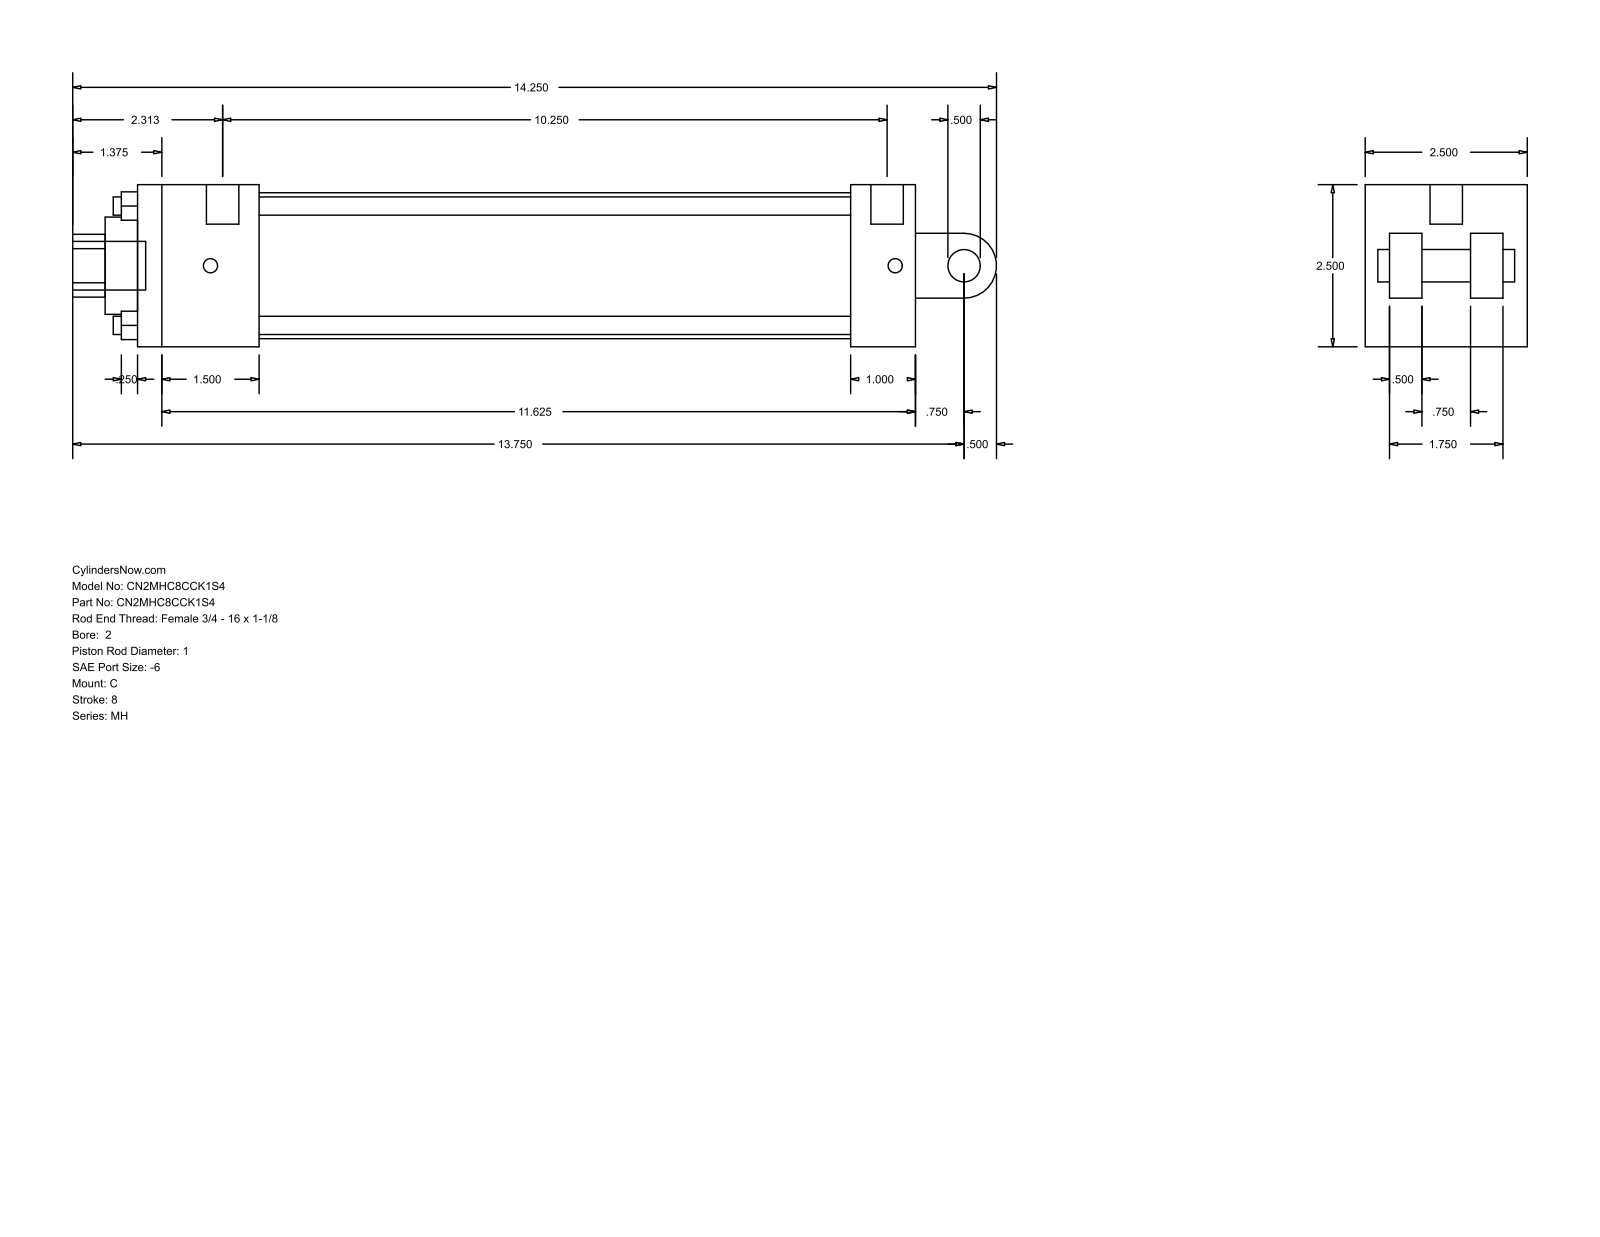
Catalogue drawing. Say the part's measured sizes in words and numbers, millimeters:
The part is named "MH_C__0200_1". Its 3-D file was written by "GSSL Pune (CONFIG_CONTROL_DESIGN)". It is 0 solids with 99 faces: 70 planar, 29 cylindrical and 0 other. Overall it measures 361.95 by 63.5 by 63.5 millimeters. Round holes: 4 of diameter 7.14, 2 of diameter 5.56, 1 of diameter 12.7, 1 of diameter 25.4, 1 of diameter 38.1, 1 of diameter 57.15. Round bosses or shafts: 2 of diameter 12.7, 2 of diameter 5.56, 1 of diameter 19.05. Partial cylindrical surfaces (rounded edges, fillets, slot ends): 1 of radius 12.29, 1 of radius 12.7. The main face-to-face distances are 63.5, 304.8, 12.7, 25.4, 9.52, 47.63, 53.98, 279.4, 231.77, 257.17. The hole center spacings are 33.05, 46.74, 66.1, 3.17.
